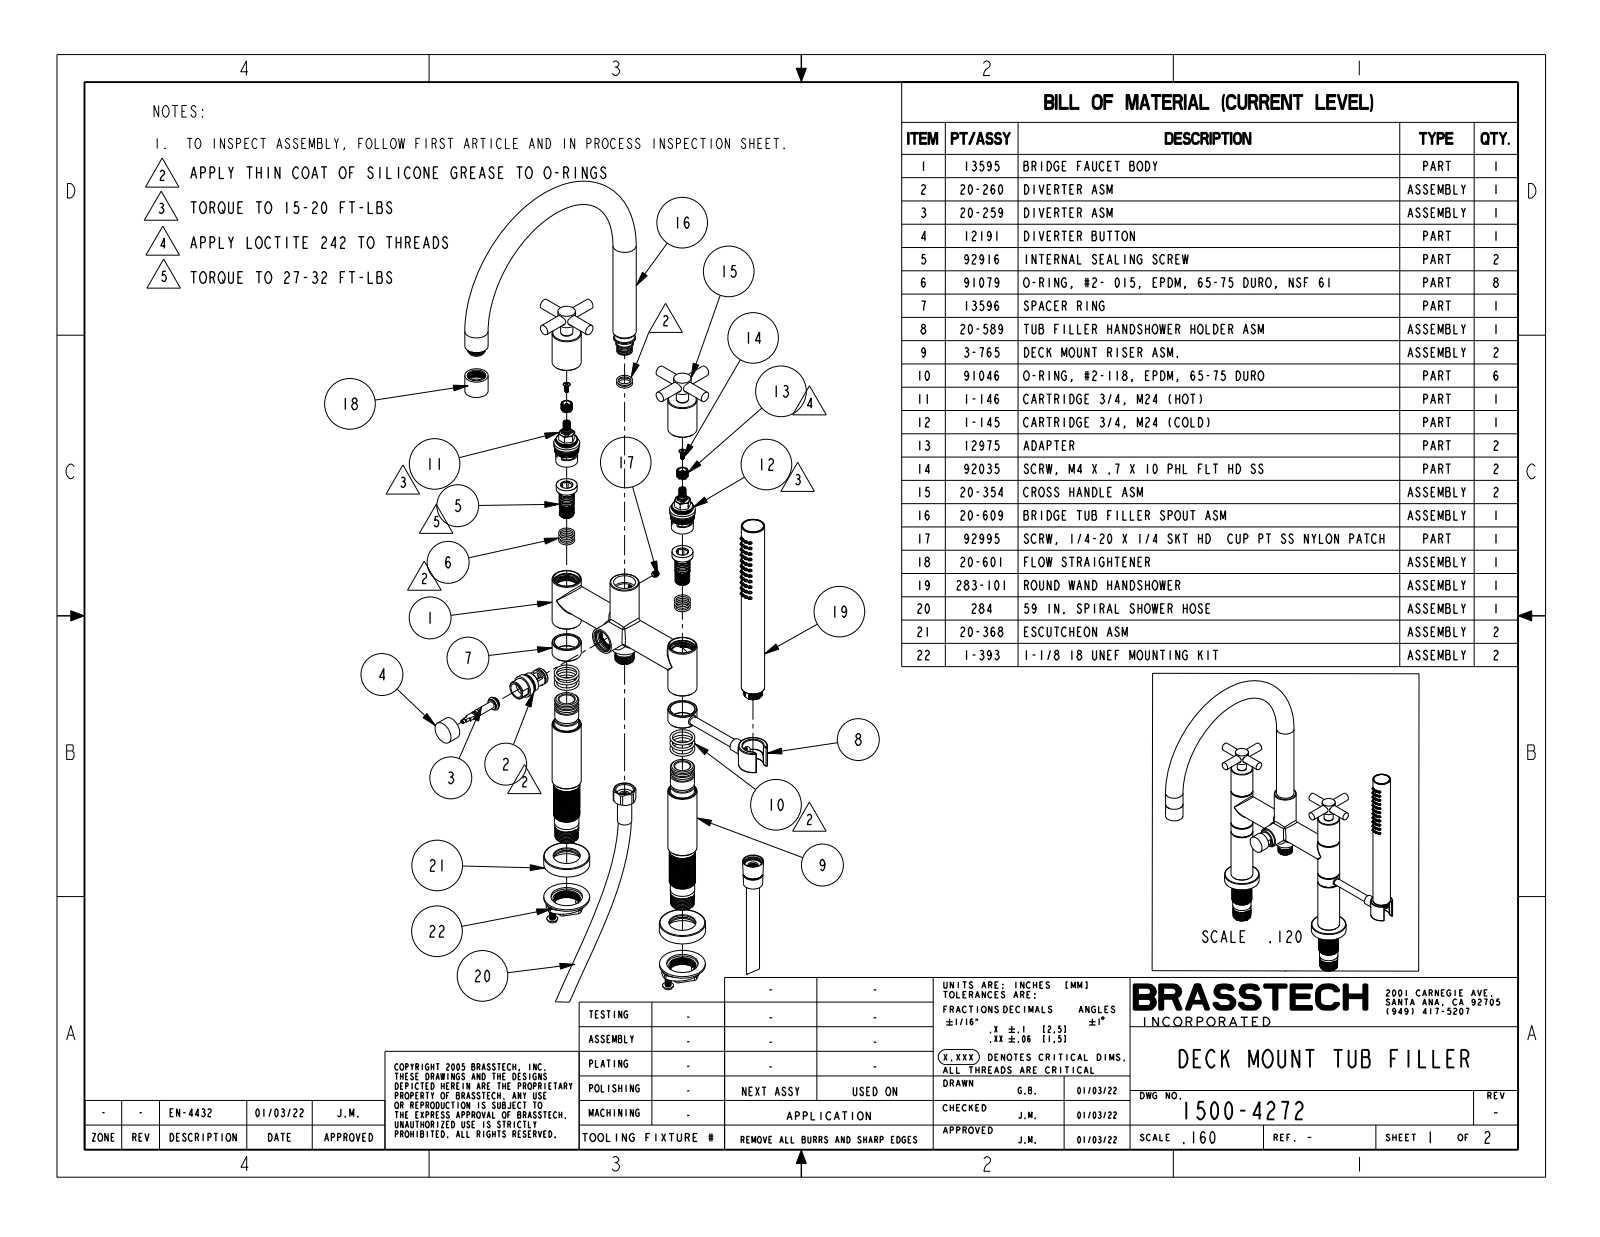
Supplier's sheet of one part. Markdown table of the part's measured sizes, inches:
| quantity | value |
| --- | --- |
| part name | 1500-4272 |
| STEP written by | CREO PARAMETRIC BY PTC INC, 2019352 (CONFIG_CONTROL_DESIGN) |
| units | inches |
| bodies | 5 solids, 1178 faces (131 planar, 321 cylindrical, 726 other) |
| overall size | 33.791 × 14.448 × 10.875 |
| volume | 71.48 in³ |
| surface area | 333.2 in² |
| round holes (diameter × count) | 0.14 × 44, 0.205 × 1, 0.691 × 1 |
| round bosses / shafts (diameter × count) | 1.25 × 5, 1 × 3, 0.75 × 3, 0.56 × 3, 0.445 × 3, 1.98 × 2, 1.15 × 2, 0.525 × 2 |
| partial cylindrical surfaces (radius × count) | 0.03 × 6, 0.41 × 1, 0.494 × 1, 0.56 × 1 |
| main face-to-face distances | 0.425, 7.84, 7.415, 7.838, 7.413, 3.613, 8.971, 8.546, 1.133, 1.131 |
| hole center spacings | 0.336, 0.604, 0.17, 0.887, 1.172, 0.29, 0.447, 0.58 |
